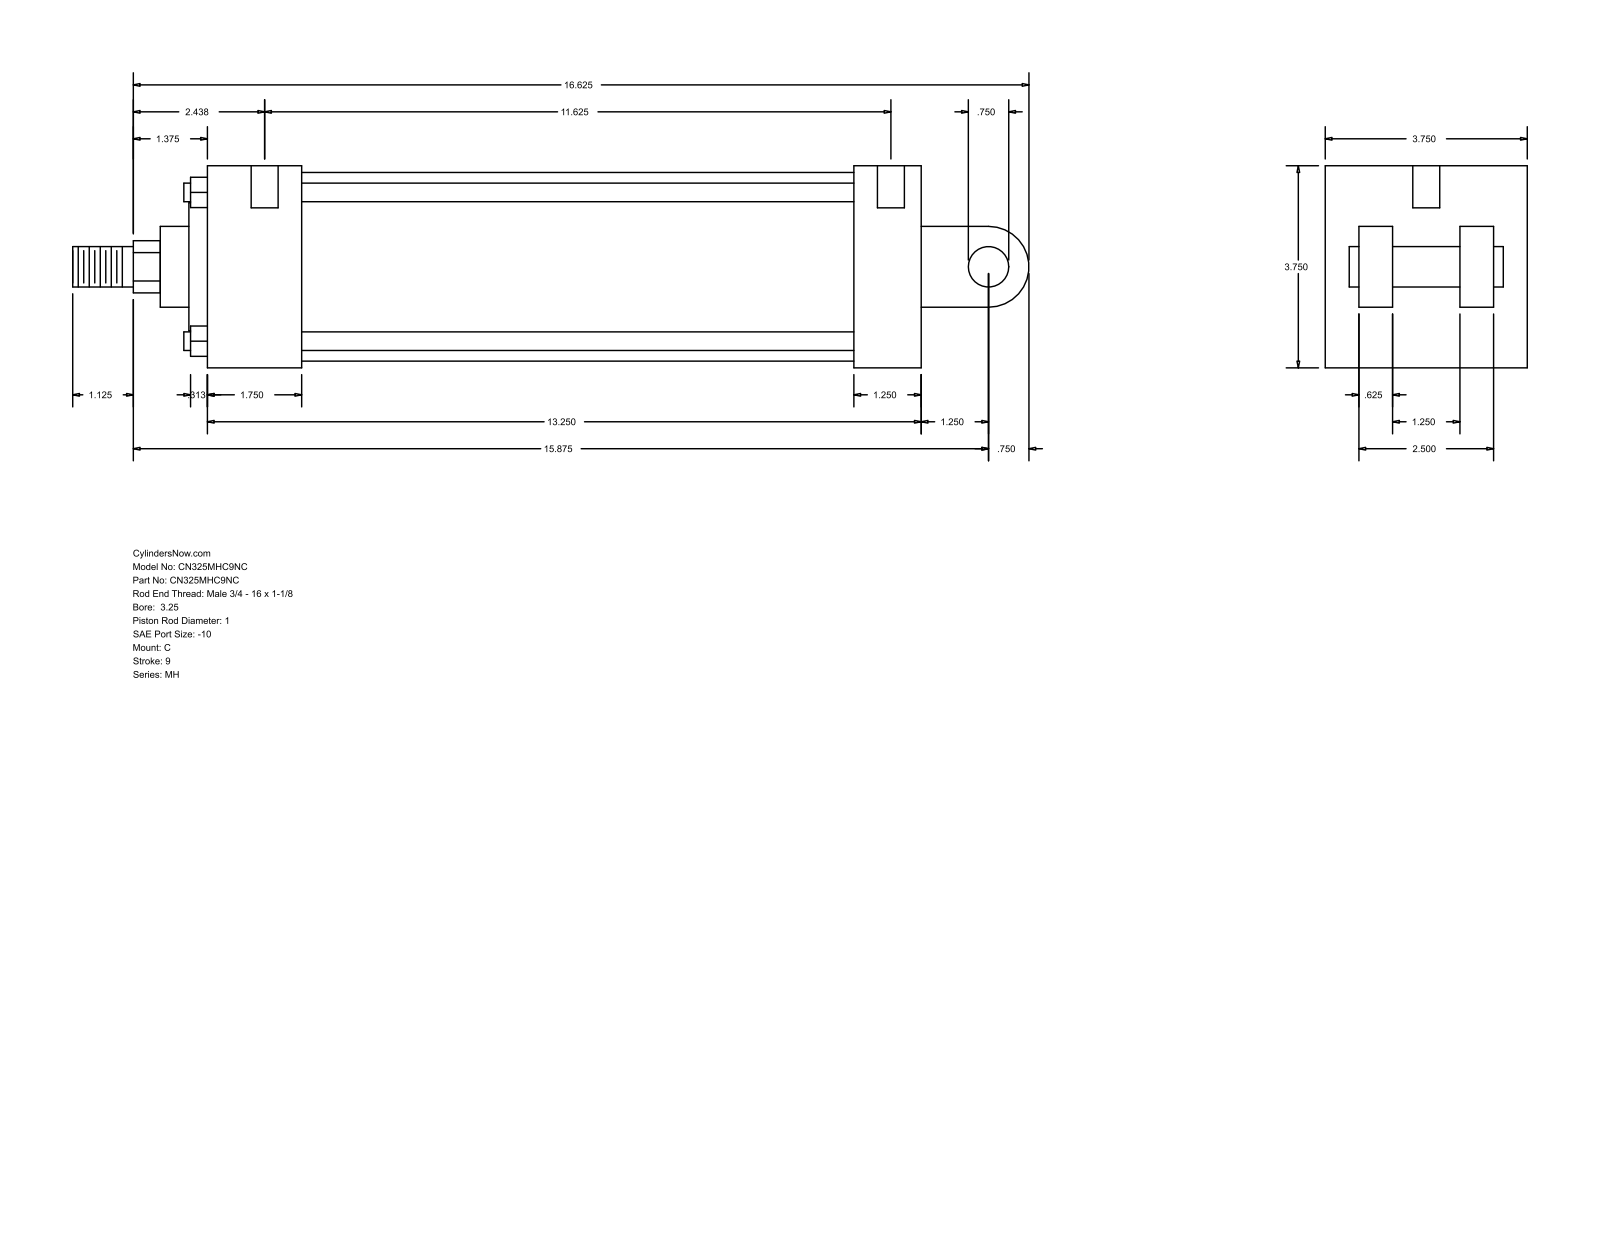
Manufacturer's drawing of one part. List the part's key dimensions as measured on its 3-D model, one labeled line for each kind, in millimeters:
Part name (STEP PRODUCT): MH_C__0325_1
STEP written by: GSSL Pune (CONFIG_CONTROL_DESIGN)
Units: millimetres
Bodies: 0 solids, 101 faces (71 planar, 30 cylindrical, 0 other)
Overall size (bounding box): 450.85 × 95.25 × 95.25
Round holes (diameter × count): ⌀5.56 ×4, ⌀12.7 ×2
Round bosses / shafts (diameter × count): ⌀8.76 ×4, ⌀19.05 ×2, ⌀88.9 ×1, ⌀60.33 ×1, ⌀38.1 ×1, ⌀25.4 ×1
Partial cylindrical surfaces — rounded edges, fillets, slot ends (radius × count): R12.29 ×1, R19.05 ×1
Main face-to-face distances: 95.24, 15.87, 336.56, 63.5, 79.37, 31.74, 47.63, 44.46, 304.81, 260.35
Hole centre spacings: 301.62, 1.58, 4.76, 295.28, 296.86, 300.04
